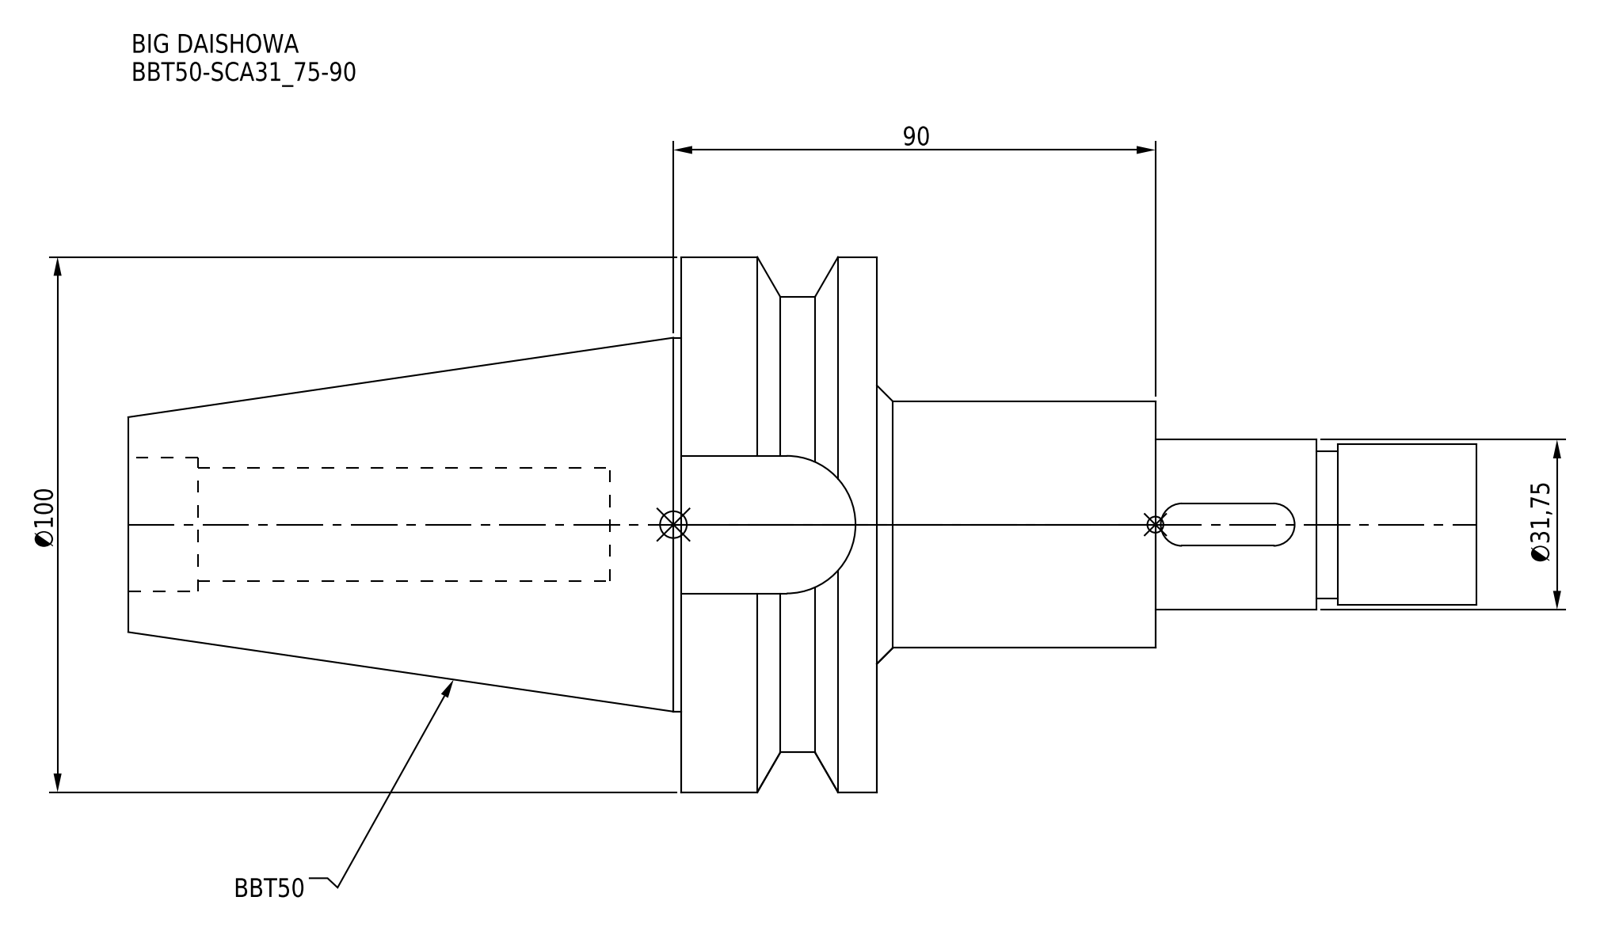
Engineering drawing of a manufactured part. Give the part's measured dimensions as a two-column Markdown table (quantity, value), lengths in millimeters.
| quantity | value |
| --- | --- |
| part name | BBT50-SCA31_75-90 |
| STEP written by | CREO PARAMETRIC BY PTC INC, 2016380 (AUTOMOTIVE_DESIGN) |
| units | millimeters |
| bodies | 1 solid, 42 faces (12 planar, 22 cylindrical, 8 other) |
| overall size | 251.8 × 100 × 100 |
| volume | 615 127 mm³ |
| surface area | 64 356 mm² |
| round holes (diameter × count) | 21.2 × 1, 25 × 1 |
| round bosses / shafts (diameter × count) | 100 × 1, 85 × 1, 69.85 × 1, 46 × 1, 31.75 × 1, 30 × 1, 27.5 × 1 |
| partial cylindrical surfaces (radius × count) | 3.96 × 2 |
| main face-to-face distances | 36.5, 52, 88.5, 191.8, 139.8, 103.3, 60, 112, 148.5, 251.8 |
